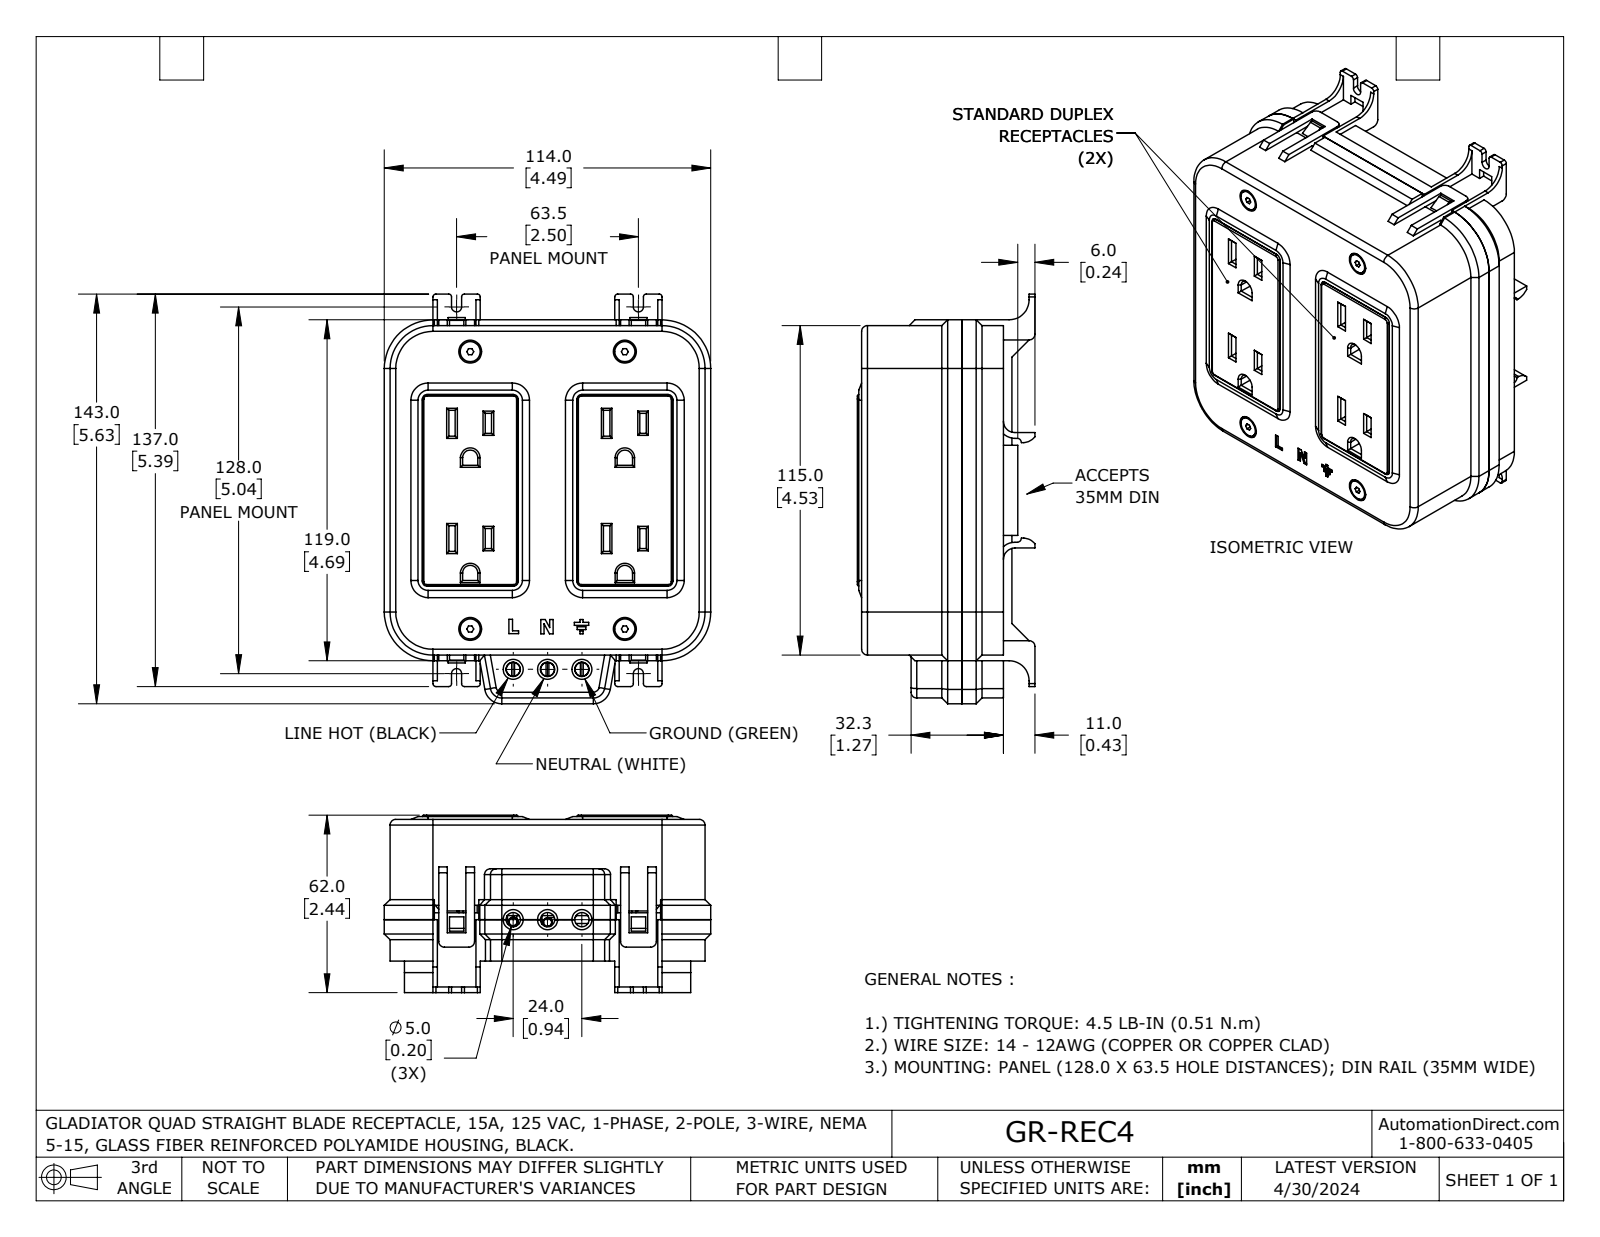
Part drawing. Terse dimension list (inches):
name: GR-REC4
written by: SolidWorks 2023 (AUTOMOTIVE_DESIGN)
unit: in
bodies: 25 solids, 2001 faces (1451 planar, 374 cylindrical, 176 other)
size: 5.63 × 4.488 × 2.441
volume: 12.6 in³; area: 234.1 in²
holes: 16× ⌀0.118, 9× ⌀0.197, 8× ⌀0.177, 4× ⌀0.11, 4× ⌀0.138, 4× ⌀0.315, 2× ⌀0.154
bosses: 14× ⌀0.276, 9× ⌀0.128, 8× ⌀0.295, 8× ⌀0.11, 6× ⌀0.189, 2× ⌀0.157, 2× ⌀0.13
rounds: 62× R0.079, 41× R0.039, 18× R0.059, 12× R0.069, 10× R0.118, 8× R0.02, 8× R0.03, 6× R0.157
face distances: 0.079, 1.87, 0.059, 0.138, 0.11, 0.039, 1.929, 2.008, 1.949, 4.252
hole spacings: 1.102, 0.472, 2.126, 0.307, 0.315, 0.787, 1.146, 1.355
